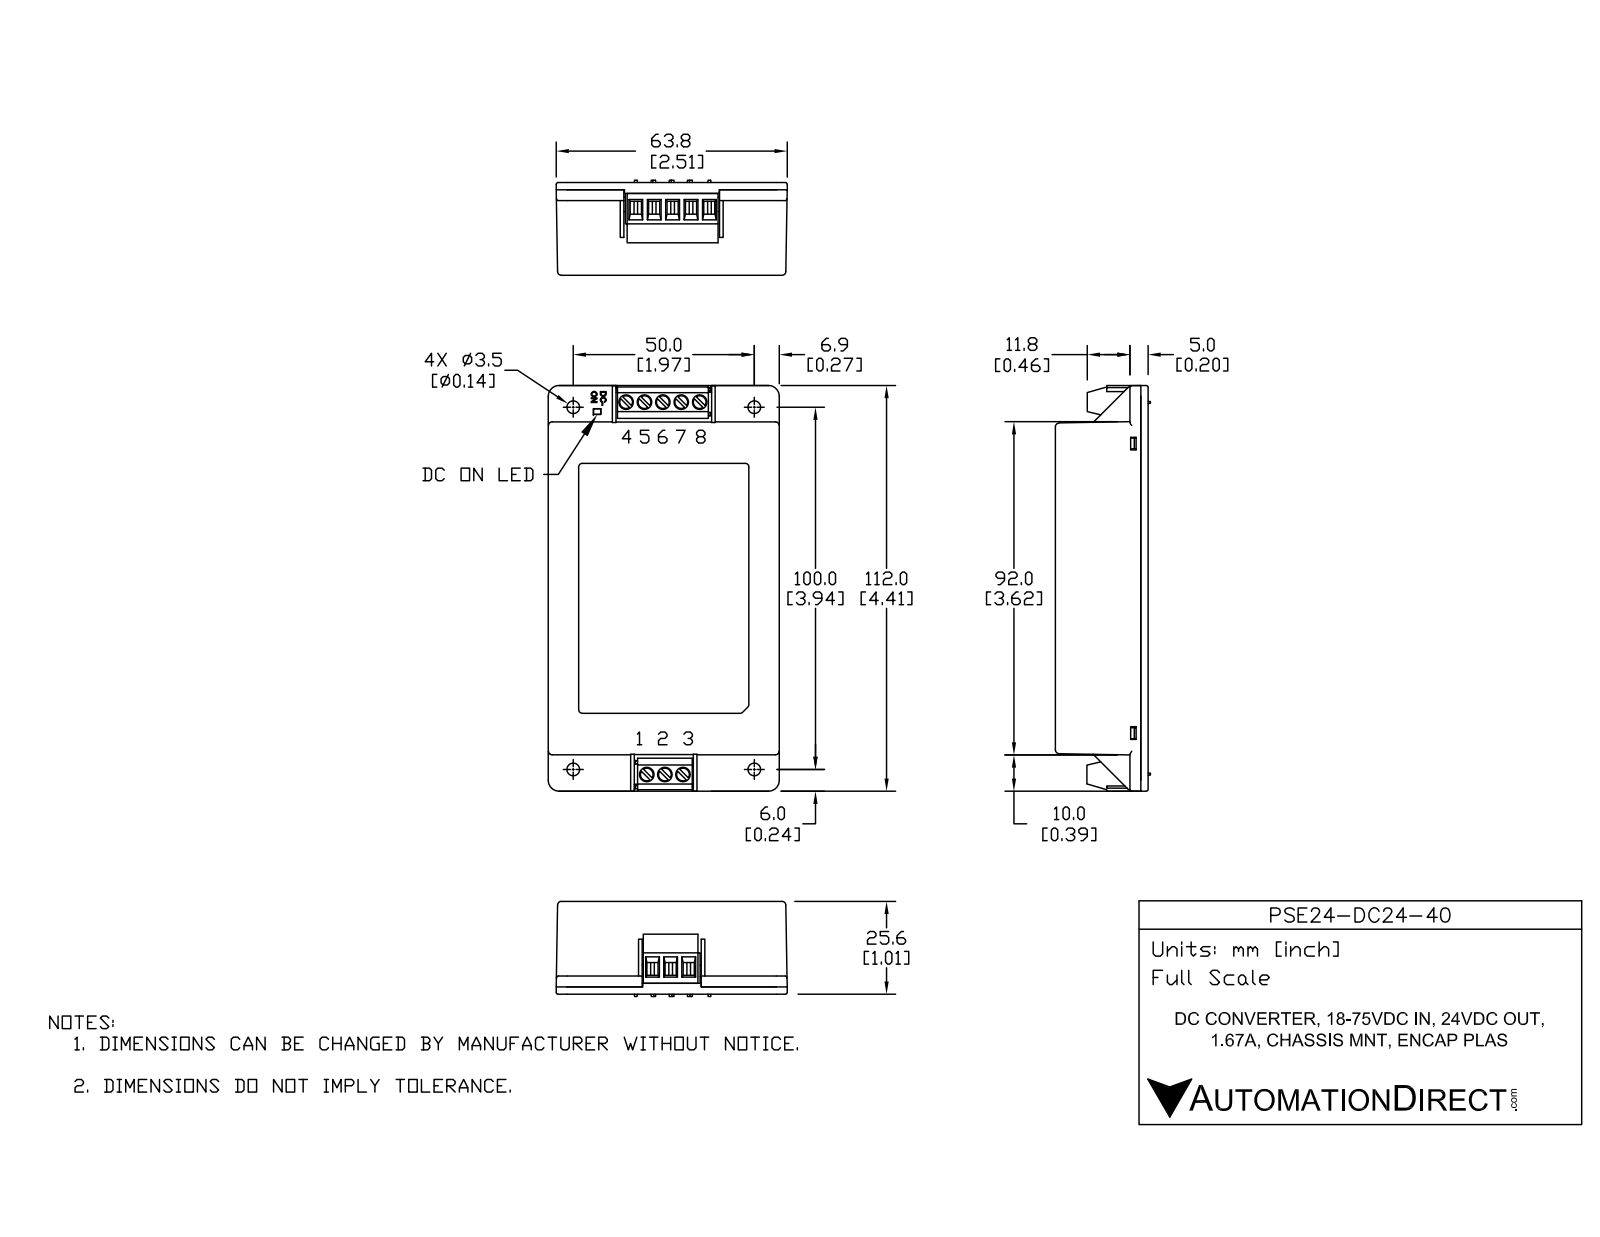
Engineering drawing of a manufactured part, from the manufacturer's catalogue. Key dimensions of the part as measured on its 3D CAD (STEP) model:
Part name (STEP PRODUCT): PSE24-DC24-40
STEP written by: SolidWorks 2019 (AUTOMOTIVE_DESIGN)
Units: millimetres
Bodies: 12 solids, 282 faces (222 planar, 54 cylindrical, 6 other)
Overall size (bounding box): 112 × 63.8 × 25.6
Volume: 158 166 mm³ · Surface area: 40 616 mm²
Round holes (diameter × count): ⌀4 ×8, ⌀3.5 ×4
Round bosses / shafts (diameter × count): ⌀3.5 ×8
Partial cylindrical surfaces — rounded edges, fillets, slot ends (radius × count): R3 ×4, R1.5 ×2
Main face-to-face distances: 2, 25.6, 23.6, 63.8, 3, 91.2, 1, 5, 20.6, 22.6
Hole centre spacings: 5.08, 10.16, 102.8, 102.9, 5, 15.24, 50, 99.9
